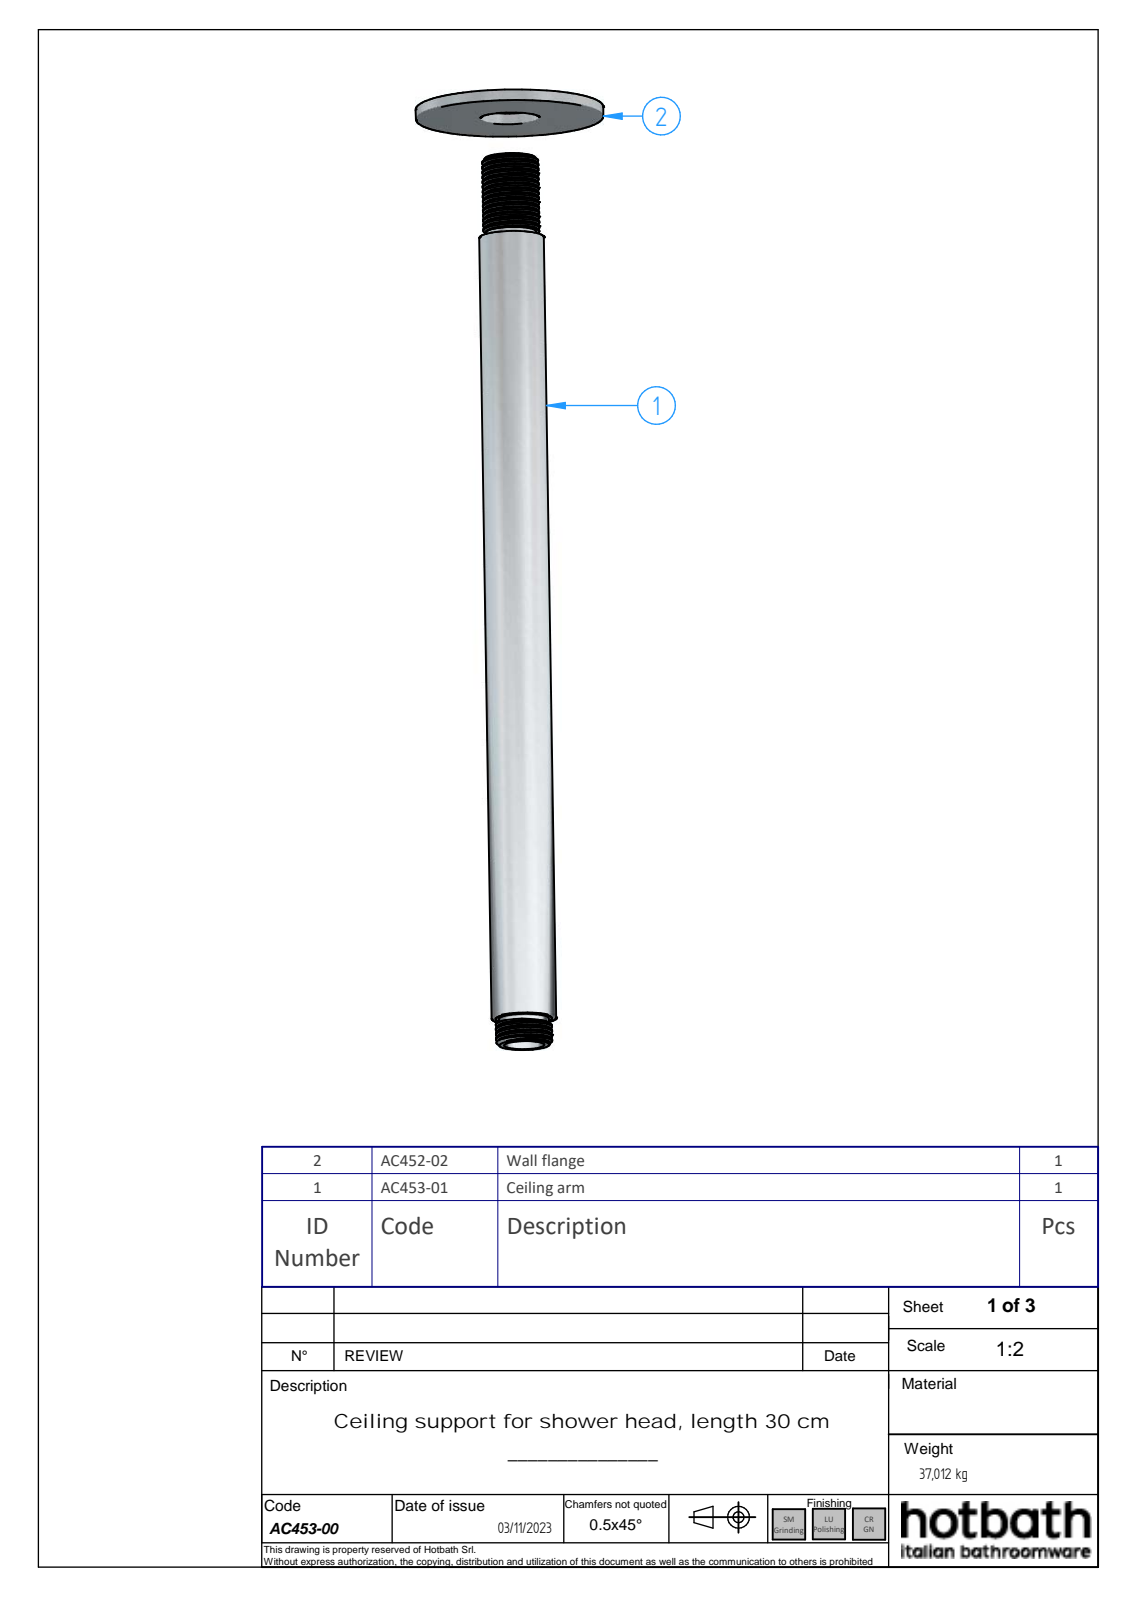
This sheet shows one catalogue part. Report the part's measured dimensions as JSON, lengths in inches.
{"part_name": "AC453-00; AC452-02; AC453-01", "step_written_by": "Solid Edge (AUTOMOTIVE_DESIGN)", "units": "inches", "bodies": {"solids": 4, "faces": 126, "planar": 28, "cylindrical": 19, "other": 79}, "overall_size": [13.228, 2.744, 2.744], "volume_in3": 3.226, "surface_area_in2": 94.21, "round_holes": [[0.591, 1], [0.827, 1], [0.858, 1]], "round_bosses_or_shafts": [[0.945, 1], [0.823, 1], [0.728, 1]], "partial_cylinders_radius": [[0.02, 4]], "face_to_face_distances": [0.157, 0.039, 0.118, 0.02, 0.098, 0.059, 11.063, 0.591, 11.811, 11.161]}
